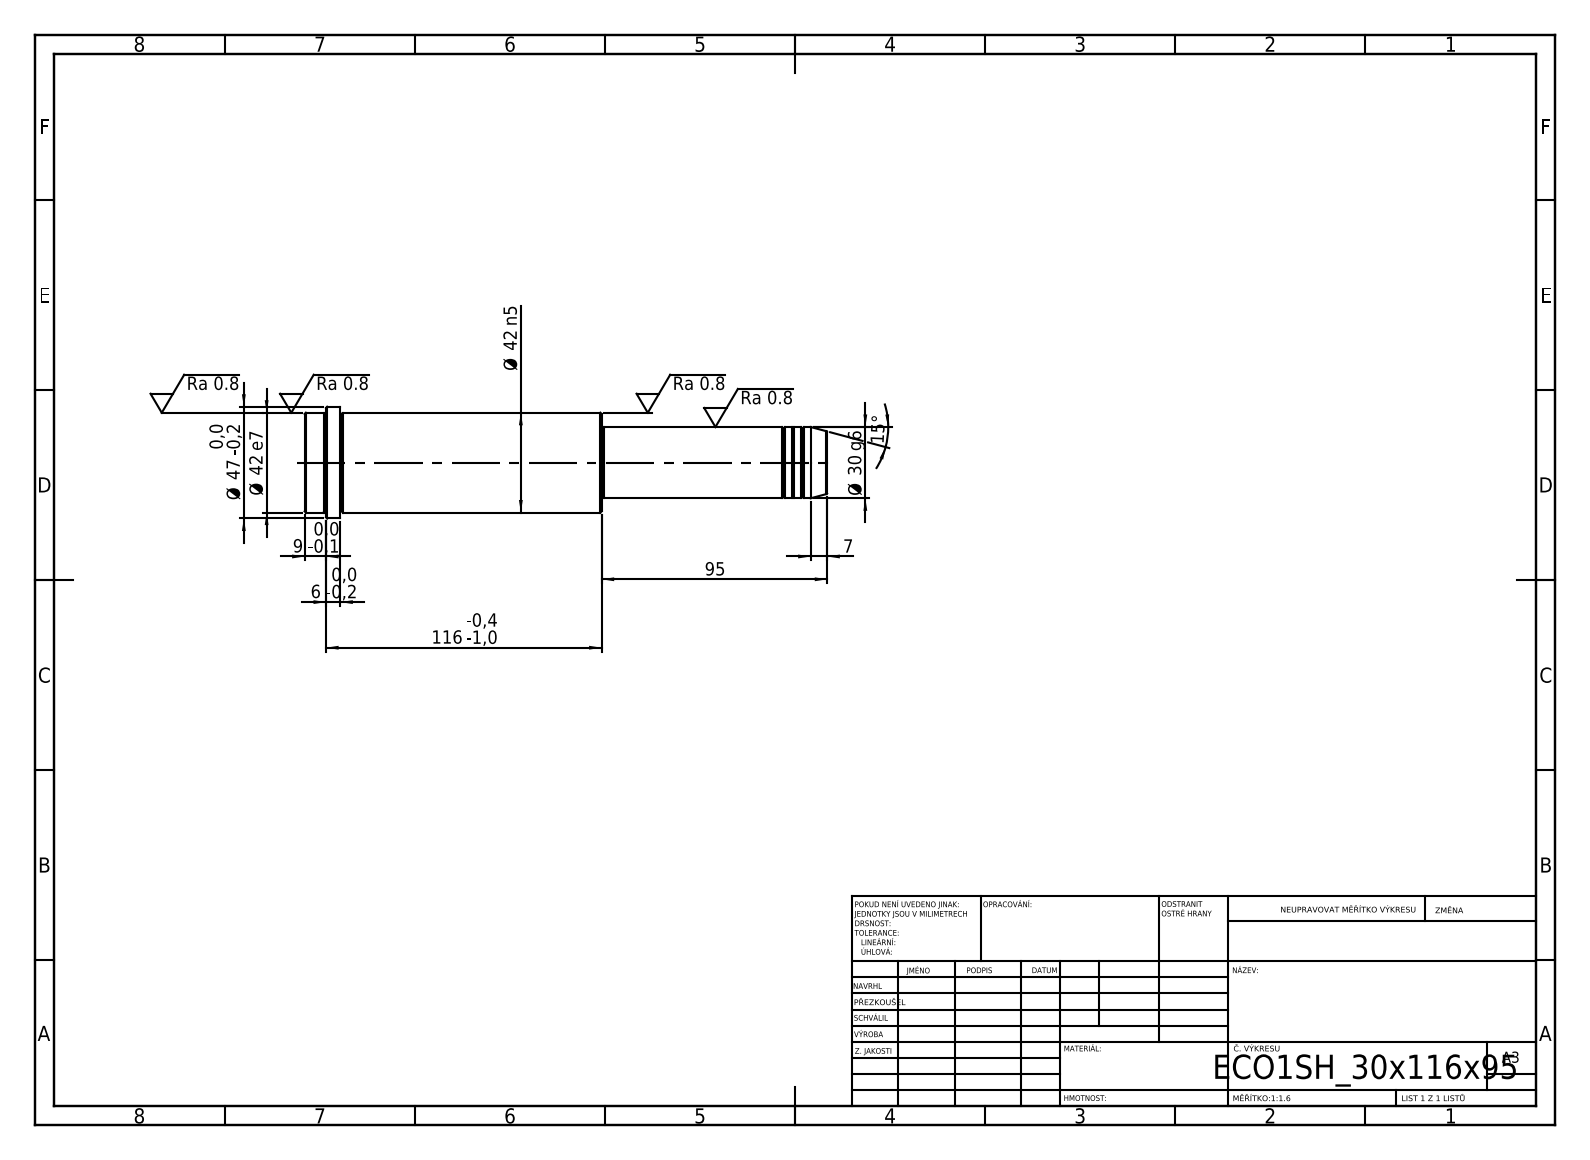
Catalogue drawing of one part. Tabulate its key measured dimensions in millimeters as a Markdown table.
| quantity | value |
| --- | --- |
| STEP written by | SolidWorks 2019 (CONFIG_CONTROL_DESIGN) |
| units | millimeters |
| bodies | 1 solid, 52 faces (6 planar, 16 cylindrical, 30 other) |
| overall size | 220 × 47 × 47 |
| volume | 241 524 mm³ |
| surface area | 29 081 mm² |
| round bosses / shafts (diameter × count) | 47 × 1, 42 × 1, 30 × 1, 29 × 1 |
| main face-to-face distances | 125, 95, 220, 205, 110, 15, 211, 116, 6, 9 |
